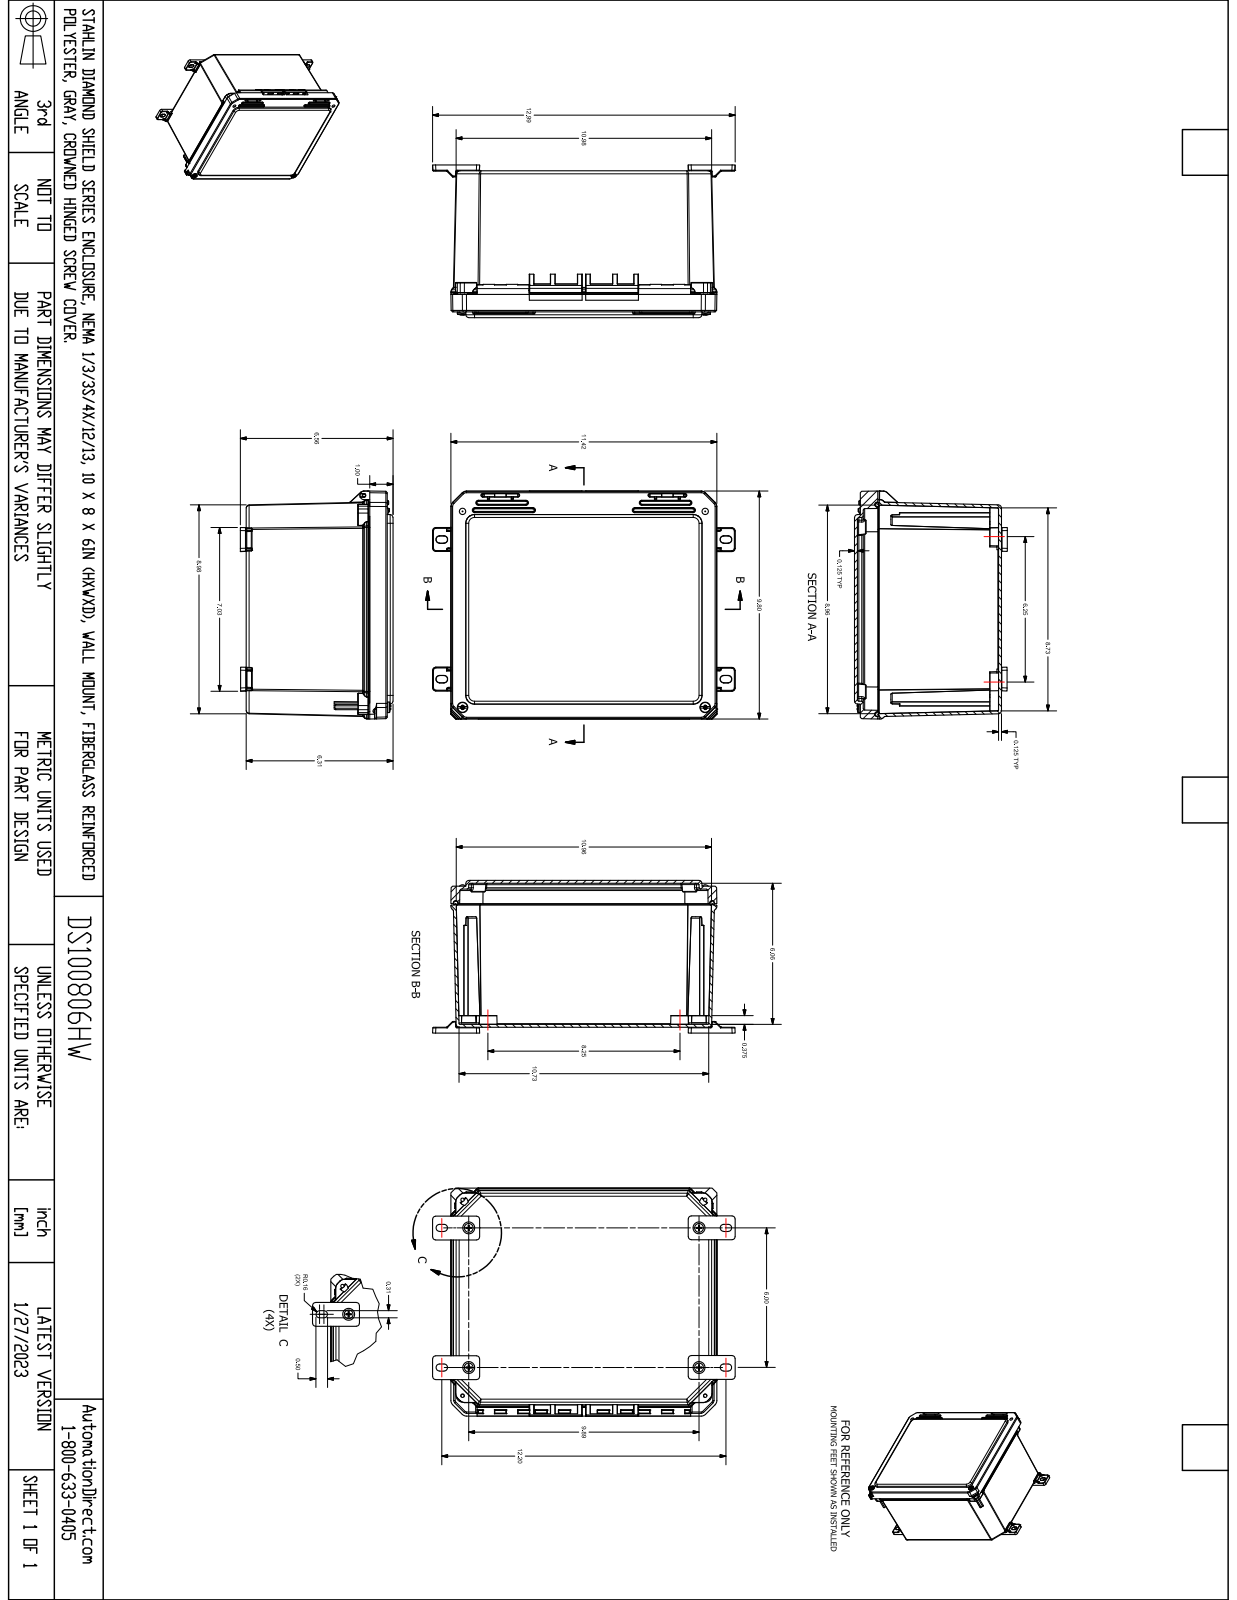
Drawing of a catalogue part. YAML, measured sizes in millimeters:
part_name: "FR100806HW"
step_written_by: "SolidWorks 2021 (AUTOMOTIVE_DESIGN)"
units: millimeters
bodies: {solids: 23, faces: 2137, planar: 637, cylindrical: 858, other: 642}
overall_size: [290.2, 249.3, 167.6]
volume: 1152000
surface_area: 633300
round_holes:
  - {diameter: 3.9, count: 8}
  - {diameter: 4, count: 8}
  - {diameter: 4, count: 4}
  - {diameter: 6.4, count: 4}
  - {diameter: 6.4, count: 4}
  - {diameter: 3.5, count: 3}
  - {diameter: 3.8, count: 2}
  - {diameter: 5.6, count: 2}
  - {diameter: 5.8, count: 2}
  - {diameter: 8, count: 2}
round_bosses_or_shafts:
  - {diameter: 6.9, count: 8}
  - {diameter: 22.1, count: 4}
  - {diameter: 6.7, count: 4}
  - {diameter: 11.4, count: 2}
  - {diameter: 5.3, count: 2}
  - {diameter: 5.1, count: 2}
  - {diameter: 3.4, count: 2}
  - {diameter: 11, count: 1}
partial_cylinders:
  - {radius: 0.3, count: 174}
  - {radius: 0.1, count: 94}
  - {radius: 0.5, count: 70}
  - {radius: 0.8, count: 49}
  - {radius: 0.8, count: 24}
  - {radius: 1.6, count: 24}
  - {radius: 2.3, count: 24}
  - {radius: 2.4, count: 24}
face_to_face_distances: [3.2, 157, 153.9, 3.2, 160.2, 3.2, 3.2, 6.4, 150.7, 6.4]
hole_center_spacings: [238.7, 264.7, 259.8, 248.3, 21.1, 157, 188.3, 230.4]
